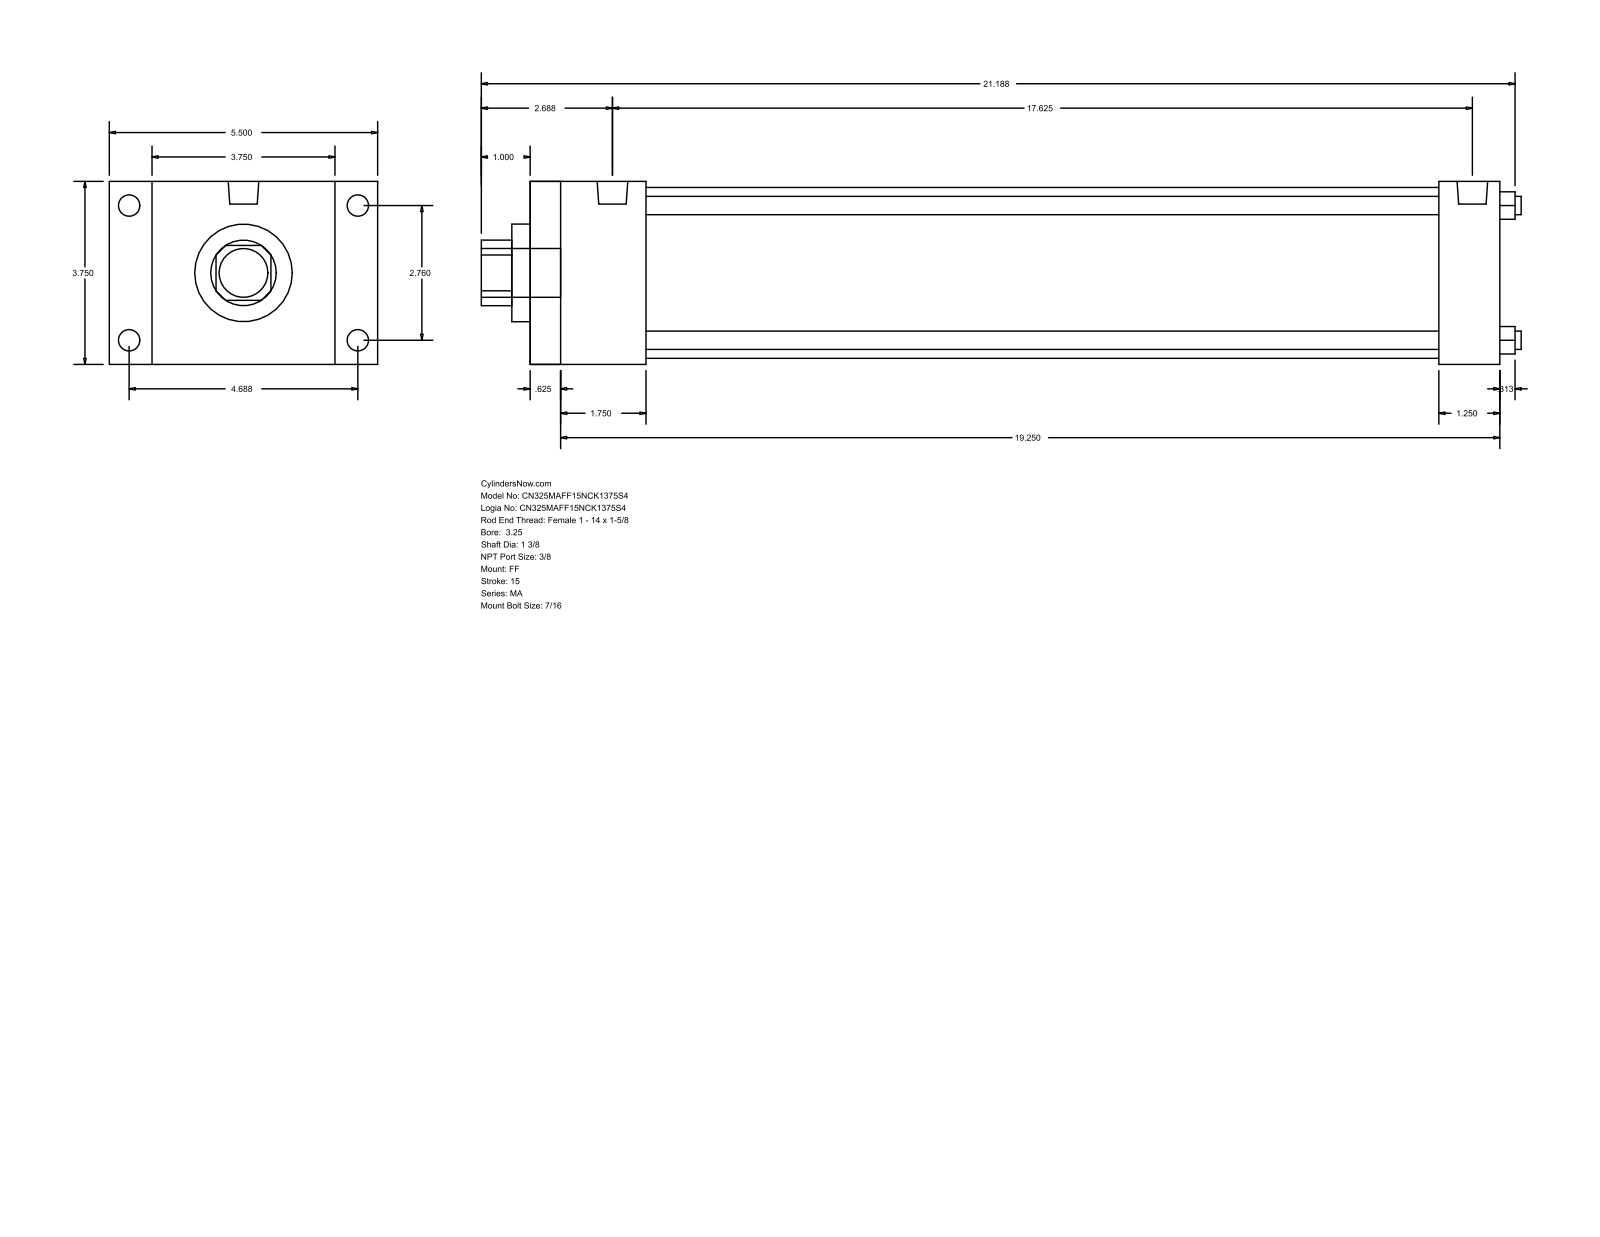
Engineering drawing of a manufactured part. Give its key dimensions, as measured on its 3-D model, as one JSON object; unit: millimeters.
{"part_name": "MA_FF__0325_1.375", "step_written_by": "GSSL Pune (CONFIG_CONTROL_DESIGN)", "units": "millimeters", "bodies": {"solids": 0, "faces": 92, "planar": 64, "cylindrical": 28, "other": 0}, "overall_size": [541.34, 139.7, 95.25], "round_holes": [[9.53, 4], [34.92, 1], [50.8, 1], [88.9, 1]], "round_bosses_or_shafts": [[11.11, 8], [15.93, 2], [25.4, 1]], "partial_cylinders_radius": [[17.06, 1]], "face_to_face_distances": [95.24, 504.83, 15.87, 488.96, 22.23, 117.47, 60.32, 473.08, 44.45, 457.21], "hole_center_spacings": [49.57, 70.1, 99.14]}
